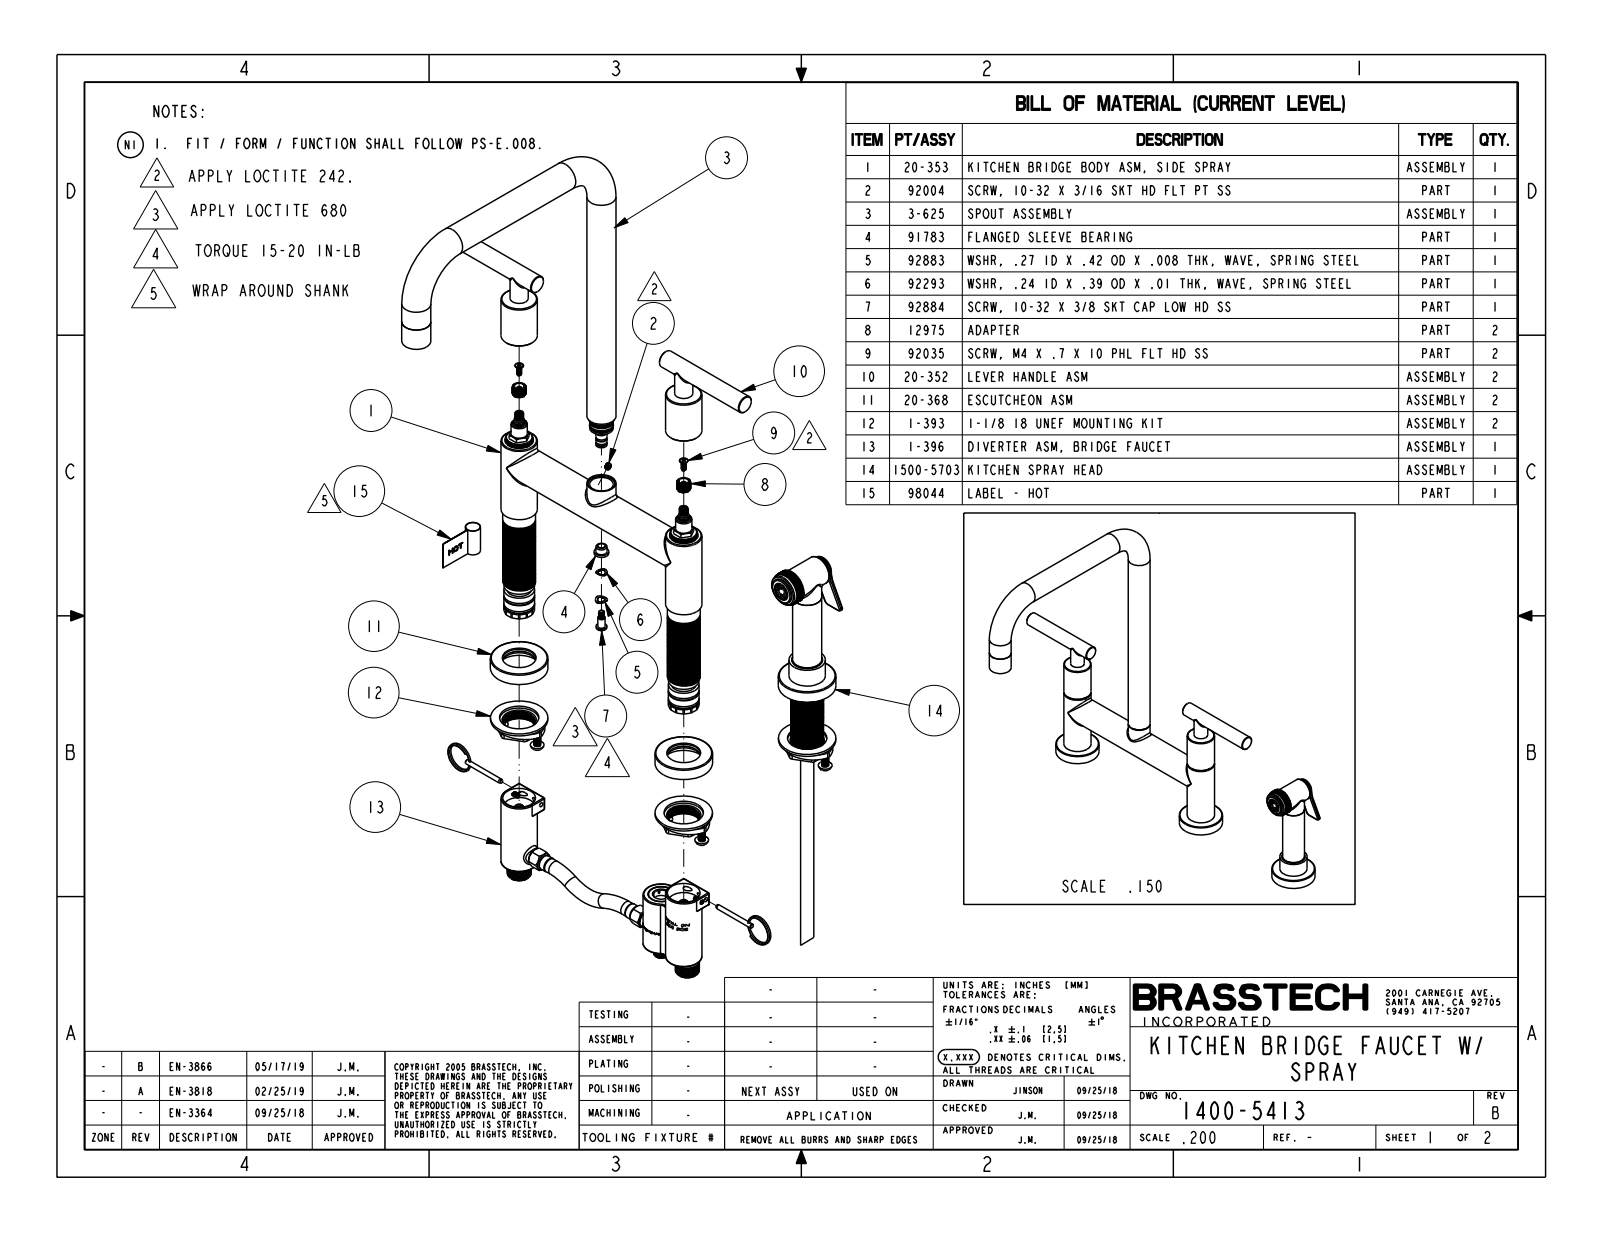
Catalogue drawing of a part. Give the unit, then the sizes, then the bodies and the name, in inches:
Units: inches
Overall size (bounding box): 17.979 × 15.019 × 10.89
Round holes (diameter × count): ⌀0.06 ×1, ⌀0.231 ×1, ⌀0.835 ×1, ⌀0.93 ×1, ⌀0.968 ×1, ⌀1.04 ×1
Round bosses / shafts (diameter × count): ⌀1.25 ×4, ⌀1 ×4, ⌀1.98 ×3, ⌀0.625 ×3, ⌀1.1 ×1, ⌀1.023 ×1, ⌀0.96 ×1, ⌀0.923 ×1
Partial cylindrical surfaces — rounded edges, fillets, slot ends (radius × count): R0.04 ×10, R0.07 ×5, R0.06 ×4, R0.156 ×2, R0.16 ×2, R0.332 ×1, R0.34 ×1, R0.385 ×1
Main face-to-face distances: 0.425, 4.892, 4.467, 0.13, 11.209, 10.784, 6.317, 3.557, 3.132, 1.335
Volume: 48.69 in³ · Surface area: 207.6 in²
Bodies: 6 solids, 664 faces (294 planar, 217 cylindrical, 153 other)
Part name (STEP PRODUCT): 1400-5413
STEP written by: CREO PARAMETRIC BY PTC INC, 2018400 (AUTOMOTIVE_DESIGN)
